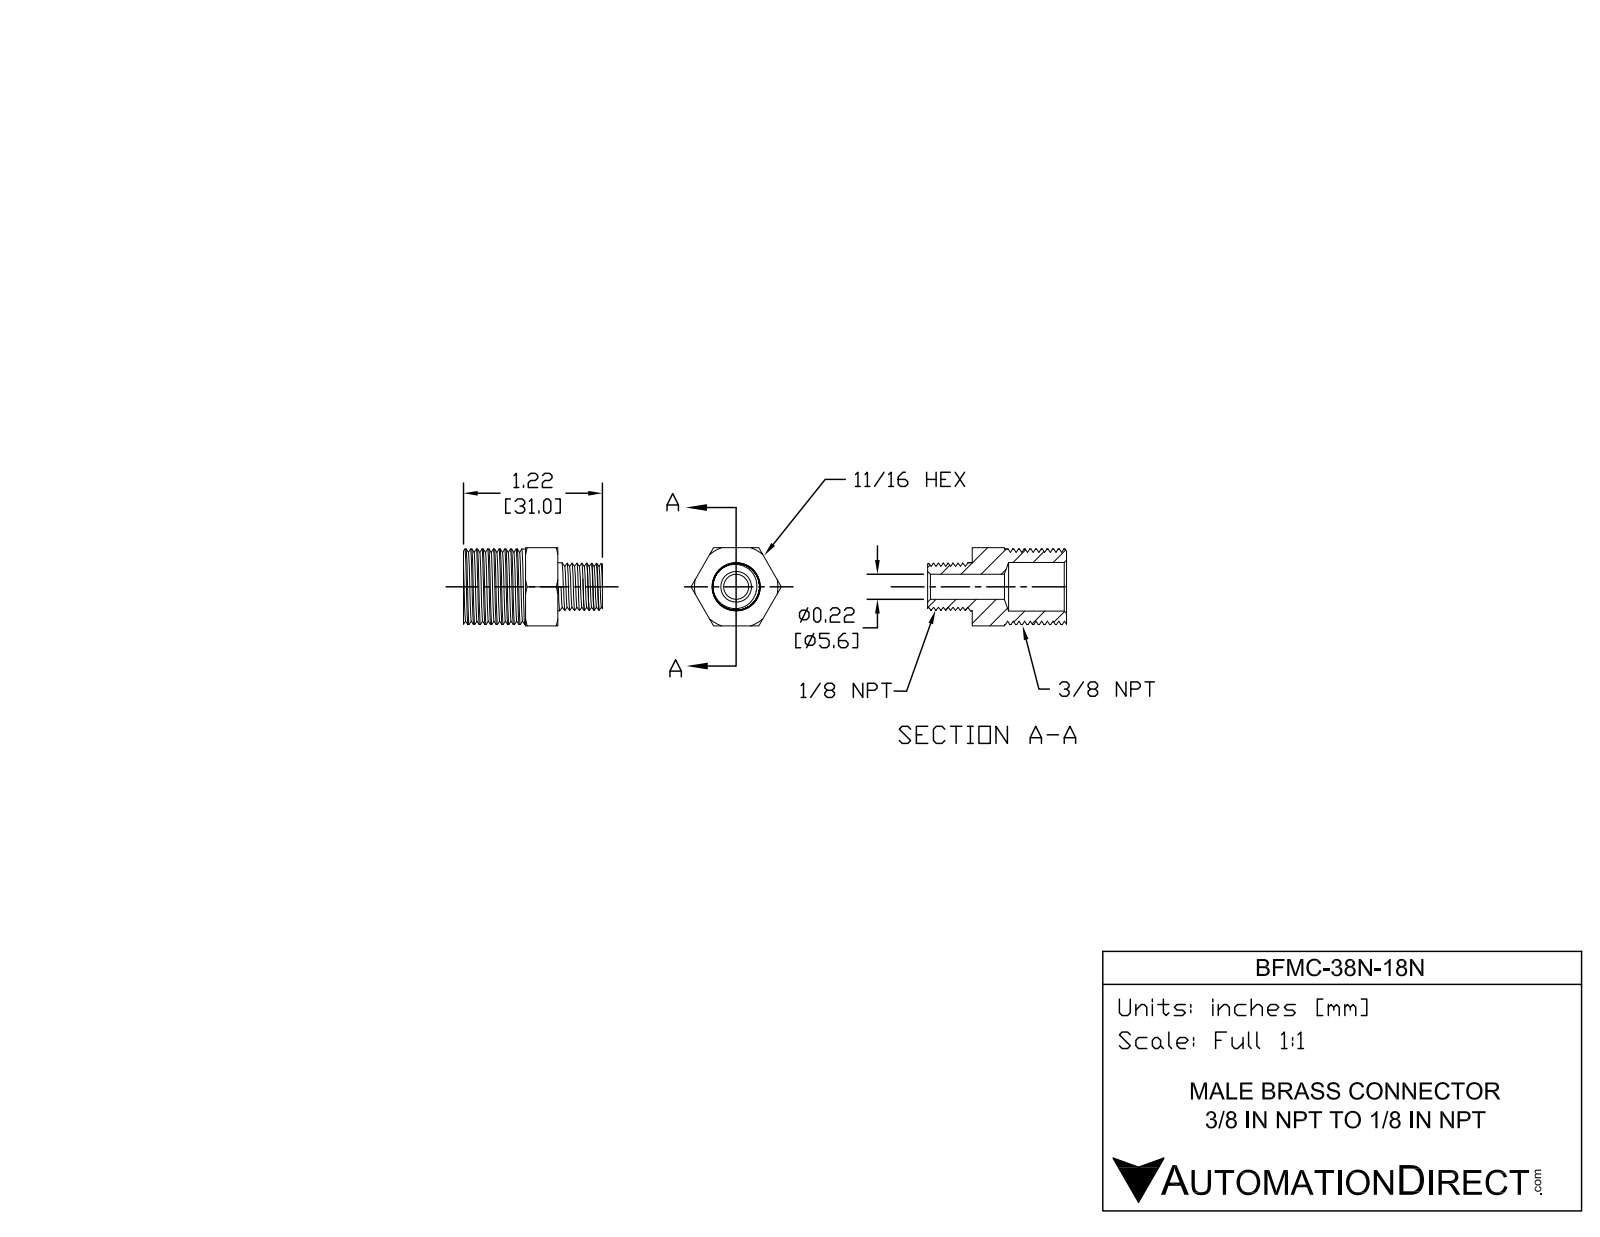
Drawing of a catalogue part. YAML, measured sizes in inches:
part_name: "BFMC-38N-18N"
step_written_by: "SolidWorks 2015 (CONFIG_CONTROL_DESIGN)"
units: inches
bodies: {solids: 1, faces: 77, planar: 14, cylindrical: 27, other: 36}
overall_size: [1.221, 0.794, 0.688]
volume: 0.236
surface_area: 5.035
round_holes:
  - {diameter: 0.22, count: 1}
  - {diameter: 0.428, count: 1}
round_bosses_or_shafts:
  - {diameter: 0.664, count: 1}
face_to_face_distances: [0.687, 0.829, 1.221, 0.392, 0.545, 0.284, 0.676, 0.344]
